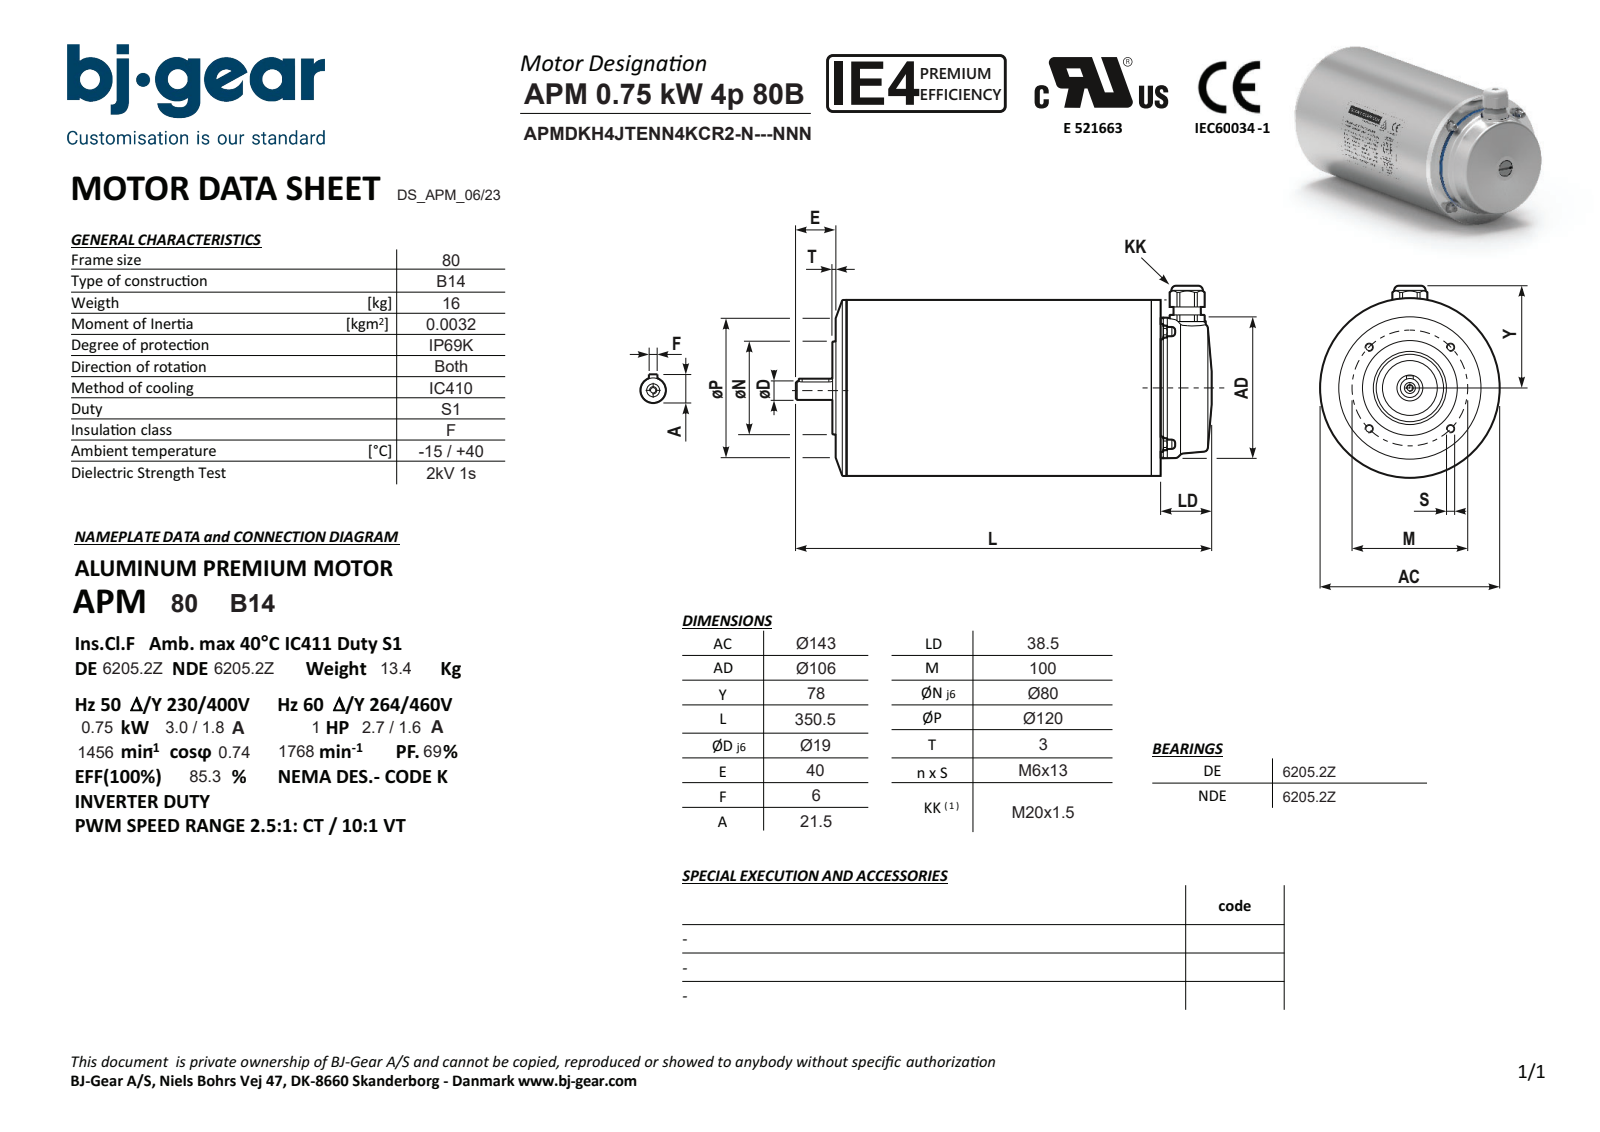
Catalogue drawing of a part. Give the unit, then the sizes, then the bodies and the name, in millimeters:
Units: millimetres
Overall size (bounding box): 350.5 × 148.3 × 142.6
Round holes (diameter × count): ⌀4.92 ×5, ⌀6.4 ×1, ⌀16 ×1, ⌀28 ×1, ⌀65 ×1
Round bosses / shafts (diameter × count): ⌀11.5 ×4, ⌀7 ×4, ⌀142.6 ×1, ⌀142.6 ×1, ⌀106 ×1, ⌀80 ×1, ⌀25 ×1, ⌀23.7 ×1
Partial cylindrical surfaces — rounded edges, fillets, slot ends (radius × count): R3 ×2, R13.2 ×1
Main face-to-face distances: 272, 6, 266, 9, 3, 275, 24, 310.5, 38.5, 304.5
Hole centre spacings: 50.01, 70.72, 100.01
Volume: 4 636 000 mm³ · Surface area: 172 344 mm²
Bodies: 1 solid, 156 faces (75 planar, 50 cylindrical, 31 other)
Part name (STEP PRODUCT): APMDKH4JTENN4KCR2-N---NNN
STEP written by: Solid Edge (AUTOMOTIVE_DESIGN)
